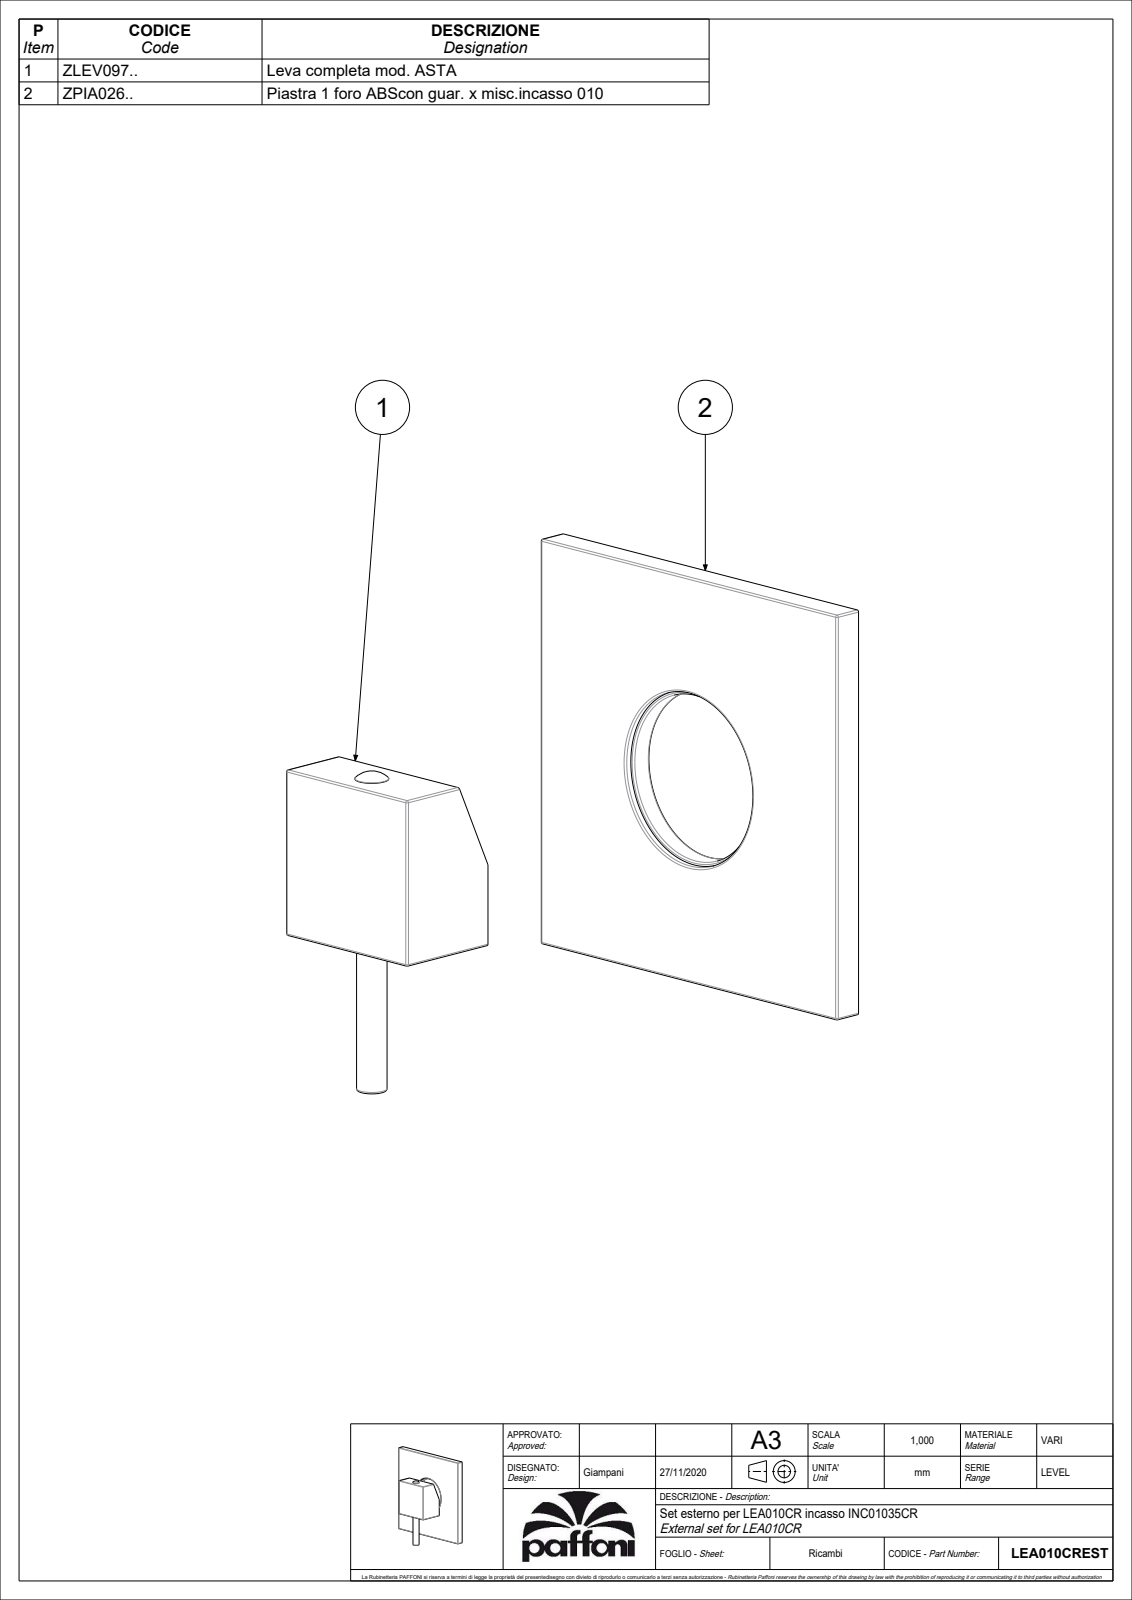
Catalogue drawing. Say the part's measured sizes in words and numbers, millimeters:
The part is named "LEA010CREST". Its 3-D file was written by "CREO PARAMETRIC BY PTC INC, 2020044 (CONFIG_CONTROL_DESIGN)". It is 2 solids with 211 faces: 101 planar, 66 cylindrical and 44 other. Overall it measures 117.5 by 110 by 40 millimeters. Its volume is 77 547 cubic millimeters and its surface area 48 978 square millimeters. Round holes: 1 of diameter 5.5, 1 of diameter 6, 1 of diameter 8.1, 1 of diameter 45, 1 of diameter 47, 1 of diameter 49. Round bosses or shafts: 1 of diameter 51, 1 of diameter 8, 1 of diameter 5. Partial cylindrical surfaces (rounded edges, fillets, slot ends): 26 of radius 0.5, 4 of radius 1, 4 of radius 2. The main face-to-face distances are 7, 2, 32.5, 77.5, 5, 30.5, 108, 75.5, 2.5, 30.
